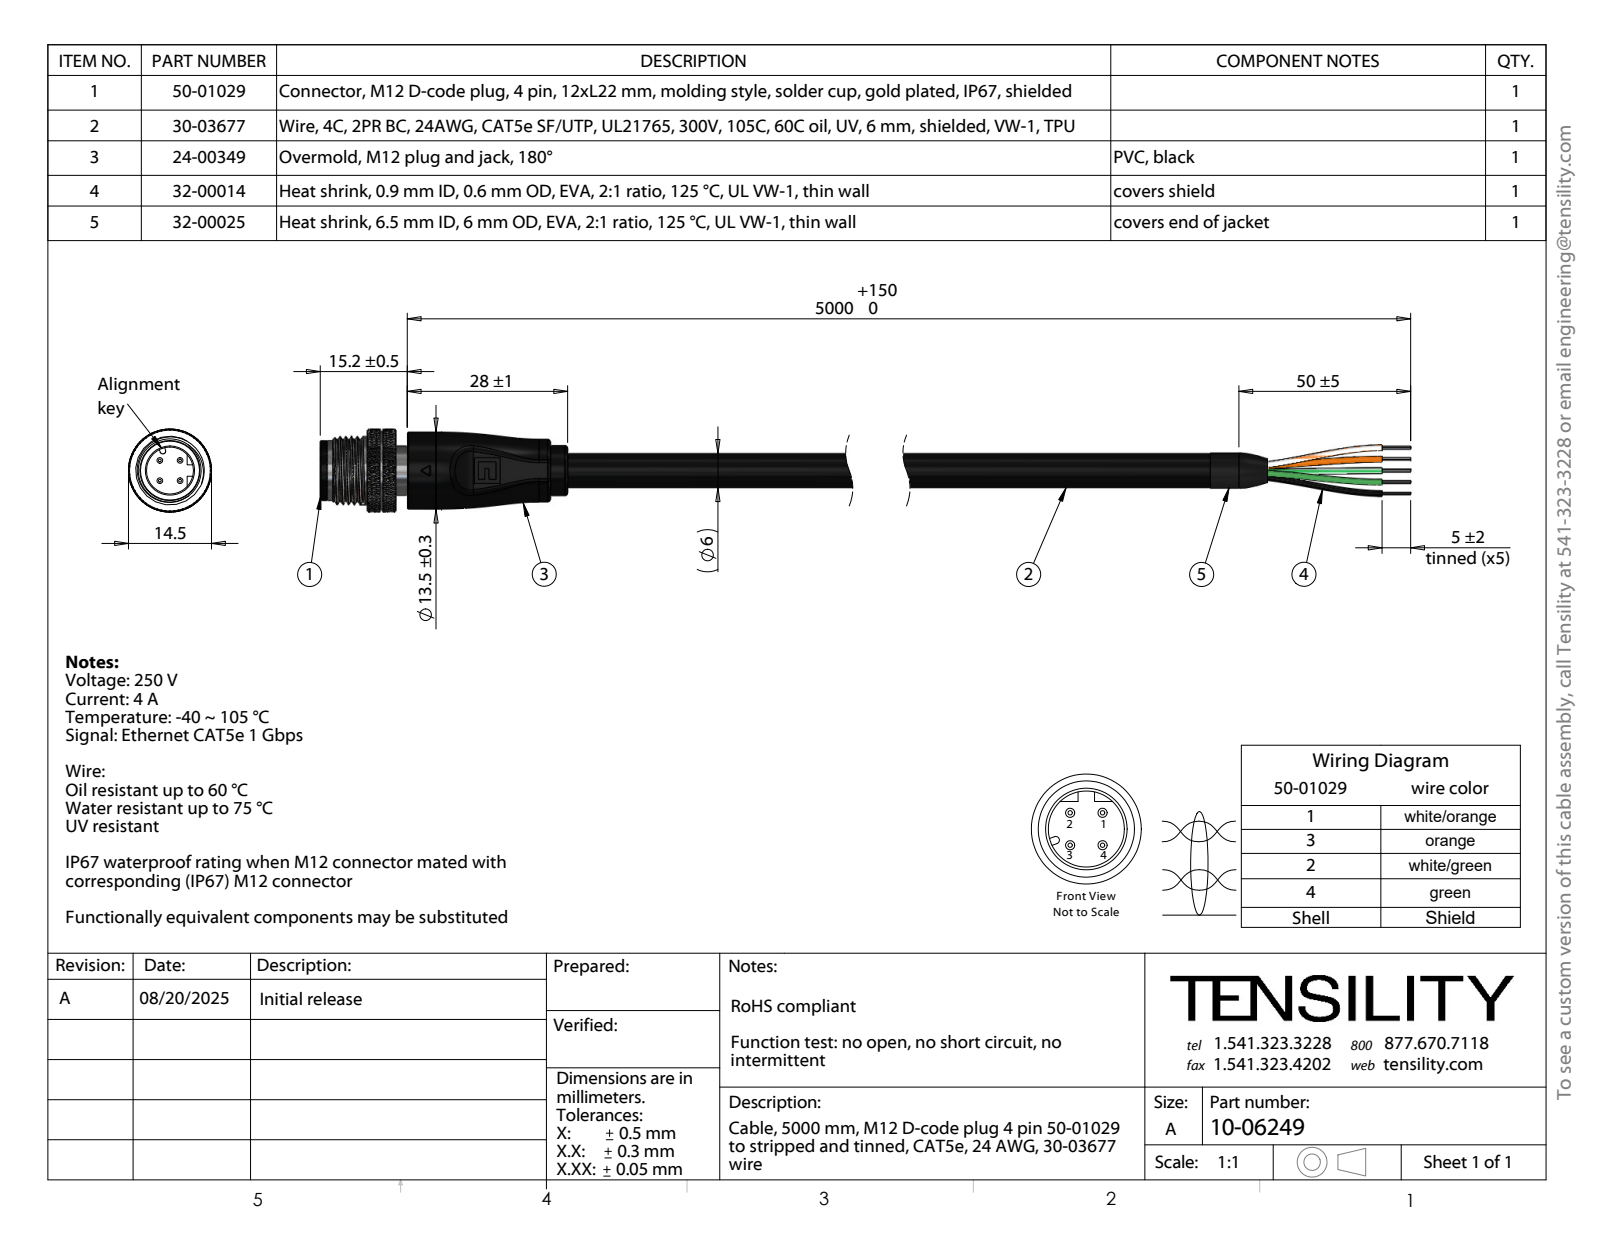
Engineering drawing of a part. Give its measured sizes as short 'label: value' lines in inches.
name: 50-01029-01_默认; 50-01029-02_默认; 24-00349_Mexico; 50-01029-04_默认 (+4 more)
written by: SolidWorks 2025 (CONFIG_CONTROL_DESIGN)
unit: in
bodies: 86 solids, 2792 faces (263 planar, 823 cylindrical, 1706 other)
size: 8.787 × 0.571 × 0.571
volume: 0.567 in³; area: 41 in²
holes: 28× ⌀0.008, 4× ⌀0.039, 4× ⌀0.041, 1× ⌀0.124, 1× ⌀0.126, 1× ⌀0.132, 1× ⌀0.315, 1× ⌀0.323, 1× ⌀0.346, 1× ⌀0.374
bosses: 35× ⌀0.008, 4× ⌀0.055, 1× ⌀0.571, 1× ⌀0.547, 1× ⌀0.531, 1× ⌀0.472, 1× ⌀0.433, 1× ⌀0.413
rounds: 2× R0.02, 2× R0.059, 2× R0.077, 1× R0.197, 1× R0.22, 1× R0.266
face distances: 7.087, 0.276, 0.079, 7.008, 0.197, 1.102, 1.181, 5.906, 0.425, 0.15
hole spacings: 0.075, 0.082, 0.042, 0.014, 0.035, 0.043, 0.049, 0.067
